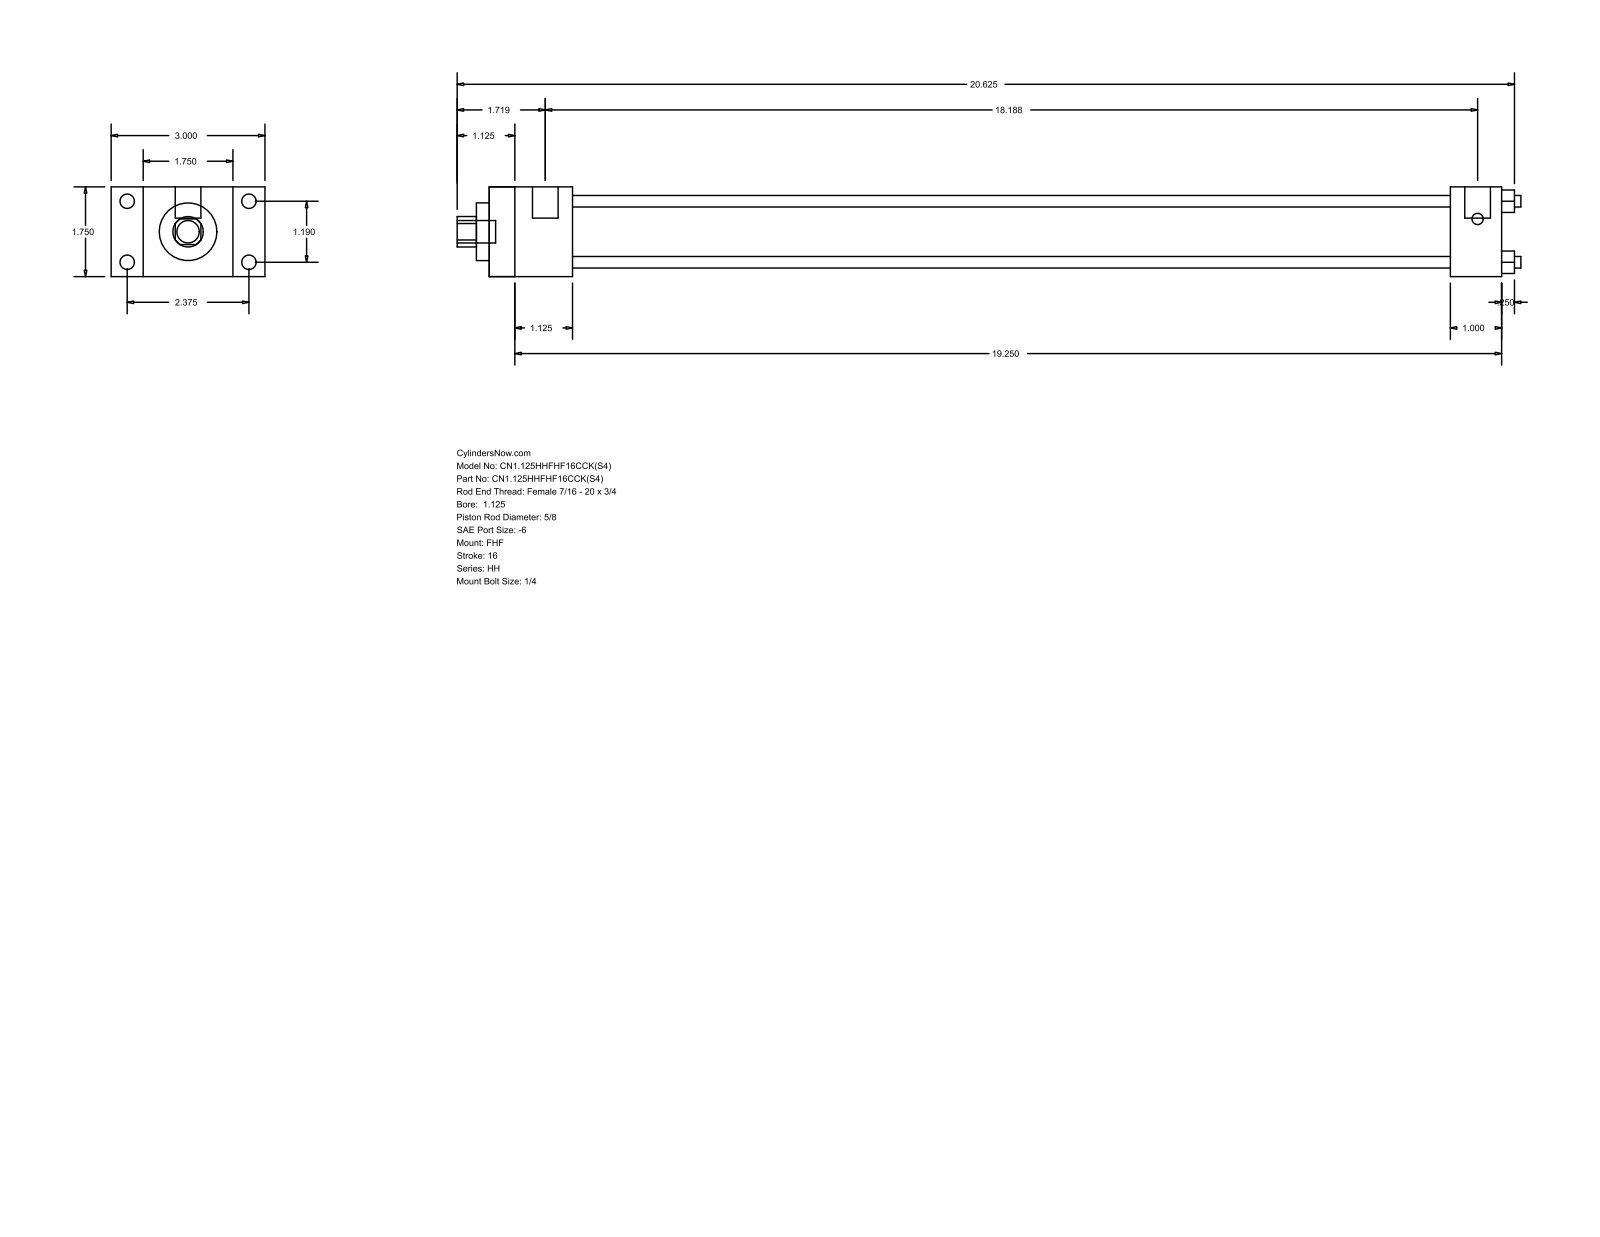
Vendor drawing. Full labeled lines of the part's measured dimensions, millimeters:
Part name (STEP PRODUCT): HH_FHF__0112_0.625
STEP written by: GSSL Pune (CONFIG_CONTROL_DESIGN)
Units: millimetres
Bodies: 0 solids, 88 faces (60 planar, 28 cylindrical, 0 other)
Overall size (bounding box): 527.05 × 76.2 × 44.45
Round holes (diameter × count): ⌀5.71 ×4, ⌀15.88 ×1, ⌀28.57 ×1, ⌀34.92 ×1
Round bosses / shafts (diameter × count): ⌀7.14 ×4, ⌀5.56 ×4, ⌀12.7 ×2, ⌀11.11 ×1
Partial cylindrical surfaces — rounded edges, fillets, slot ends (radius × count): R7.54 ×1
Main face-to-face distances: 44.46, 15.87, 60.33, 41.27, 76.2, 501.64, 460.37, 476.24, 434.97, 25.4
Hole centre spacings: 21.37, 30.22, 42.74
